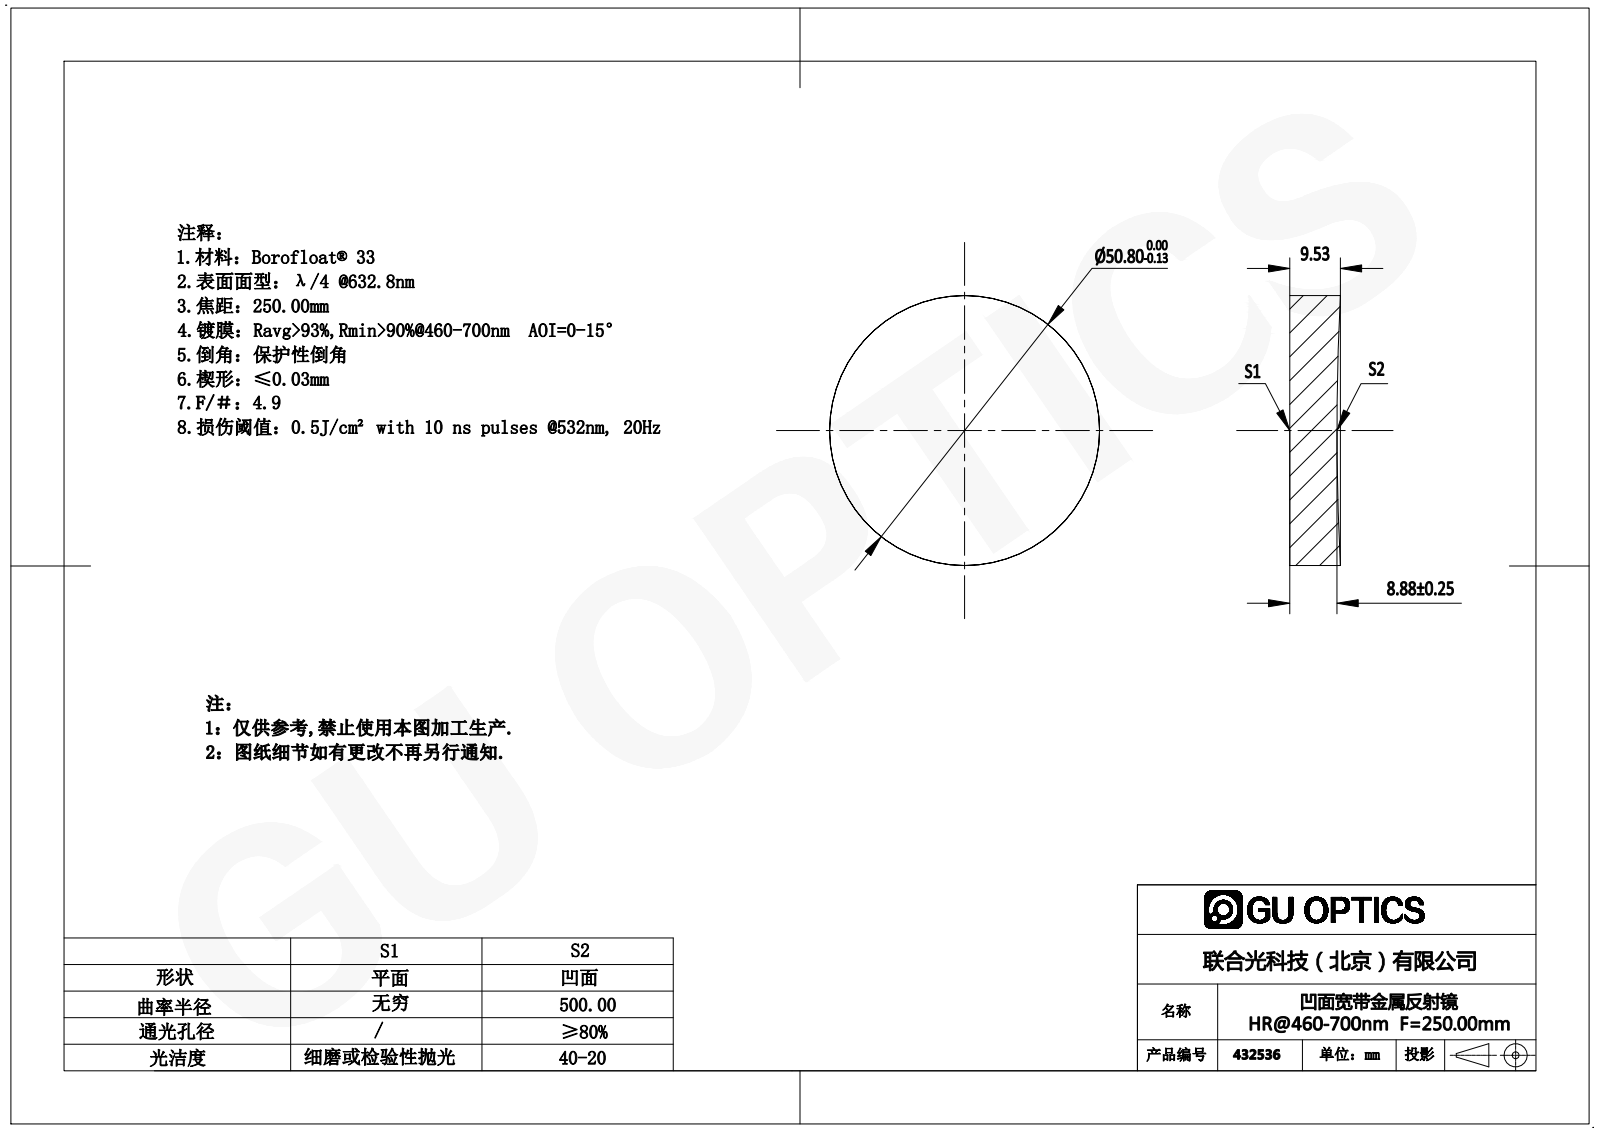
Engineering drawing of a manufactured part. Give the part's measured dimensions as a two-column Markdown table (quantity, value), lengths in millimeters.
| quantity | value |
| --- | --- |
| part name | 432532 |
| STEP written by | SolidWorks 2016 (AUTOMOTIVE_DESIGN) |
| units | millimeters |
| bodies | 1 solid, 5 faces (1 planar, 2 cylindrical, 2 other) |
| overall size | 50.8 × 50.8 × 9.53 |
| volume | 18 652 mm³ |
| surface area | 5 575 mm² |
| round bosses / shafts (diameter × count) | 50.8 × 1 |
